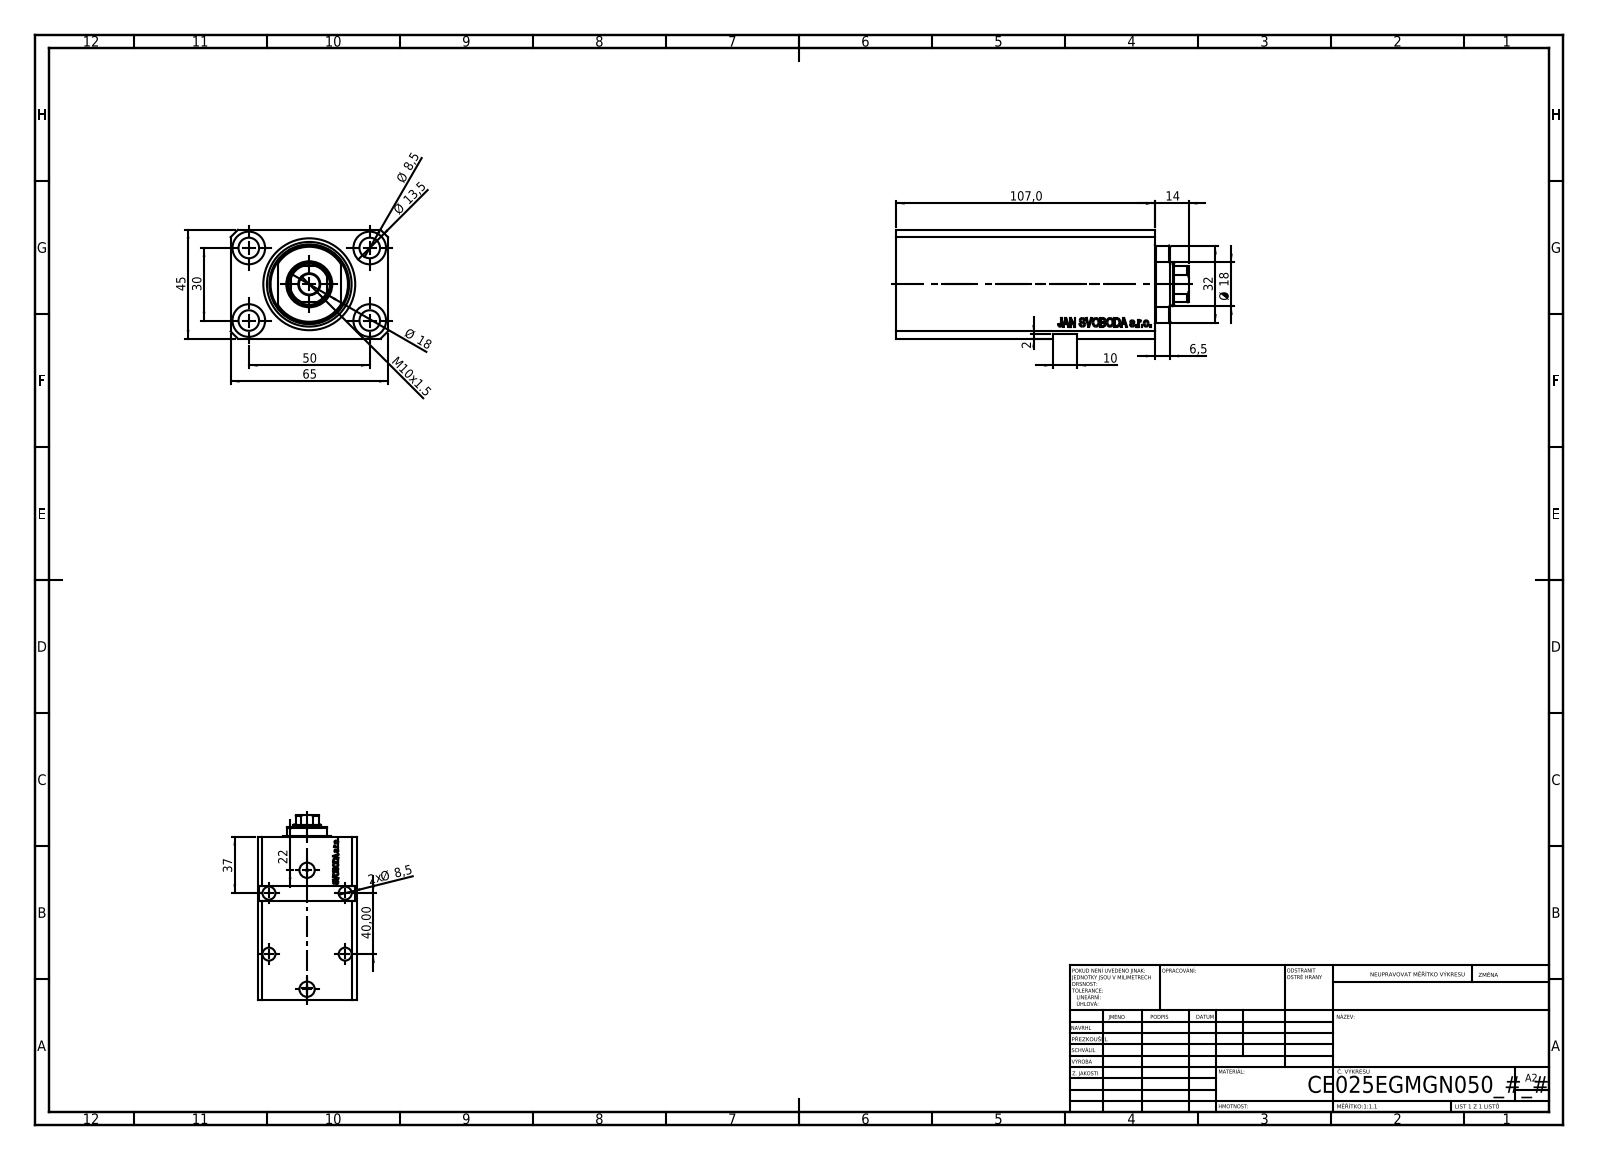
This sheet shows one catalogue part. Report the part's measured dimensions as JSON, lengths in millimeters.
{"part_name": "V250CE_E_Body; V250CE_VC_E; V250CE_C_VCP", "step_written_by": "SolidWorks 2019 (CONFIG_CONTROL_DESIGN)", "units": "millimeters", "bodies": {"solids": 3, "faces": 917, "planar": 435, "cylindrical": 104, "other": 378}, "overall_size": [121, 65, 45], "volume_mm3": 261553, "surface_area_mm2": 66925, "round_holes": [[8.5, 9], [1.25, 4], [13.5, 4], [10, 2], [13.16, 2], [20, 2], [18, 1], [25, 1], [38, 1]], "partial_cylinders_radius": [[8.5, 1], [16, 1]], "face_to_face_distances": [45, 65, 93, 14, 107, 6.9, 86.1, 100.1, 43, 9], "hole_center_spacings": [29.15, 50, 30, 33.61, 33.97, 40, 58.31, 60.42]}
